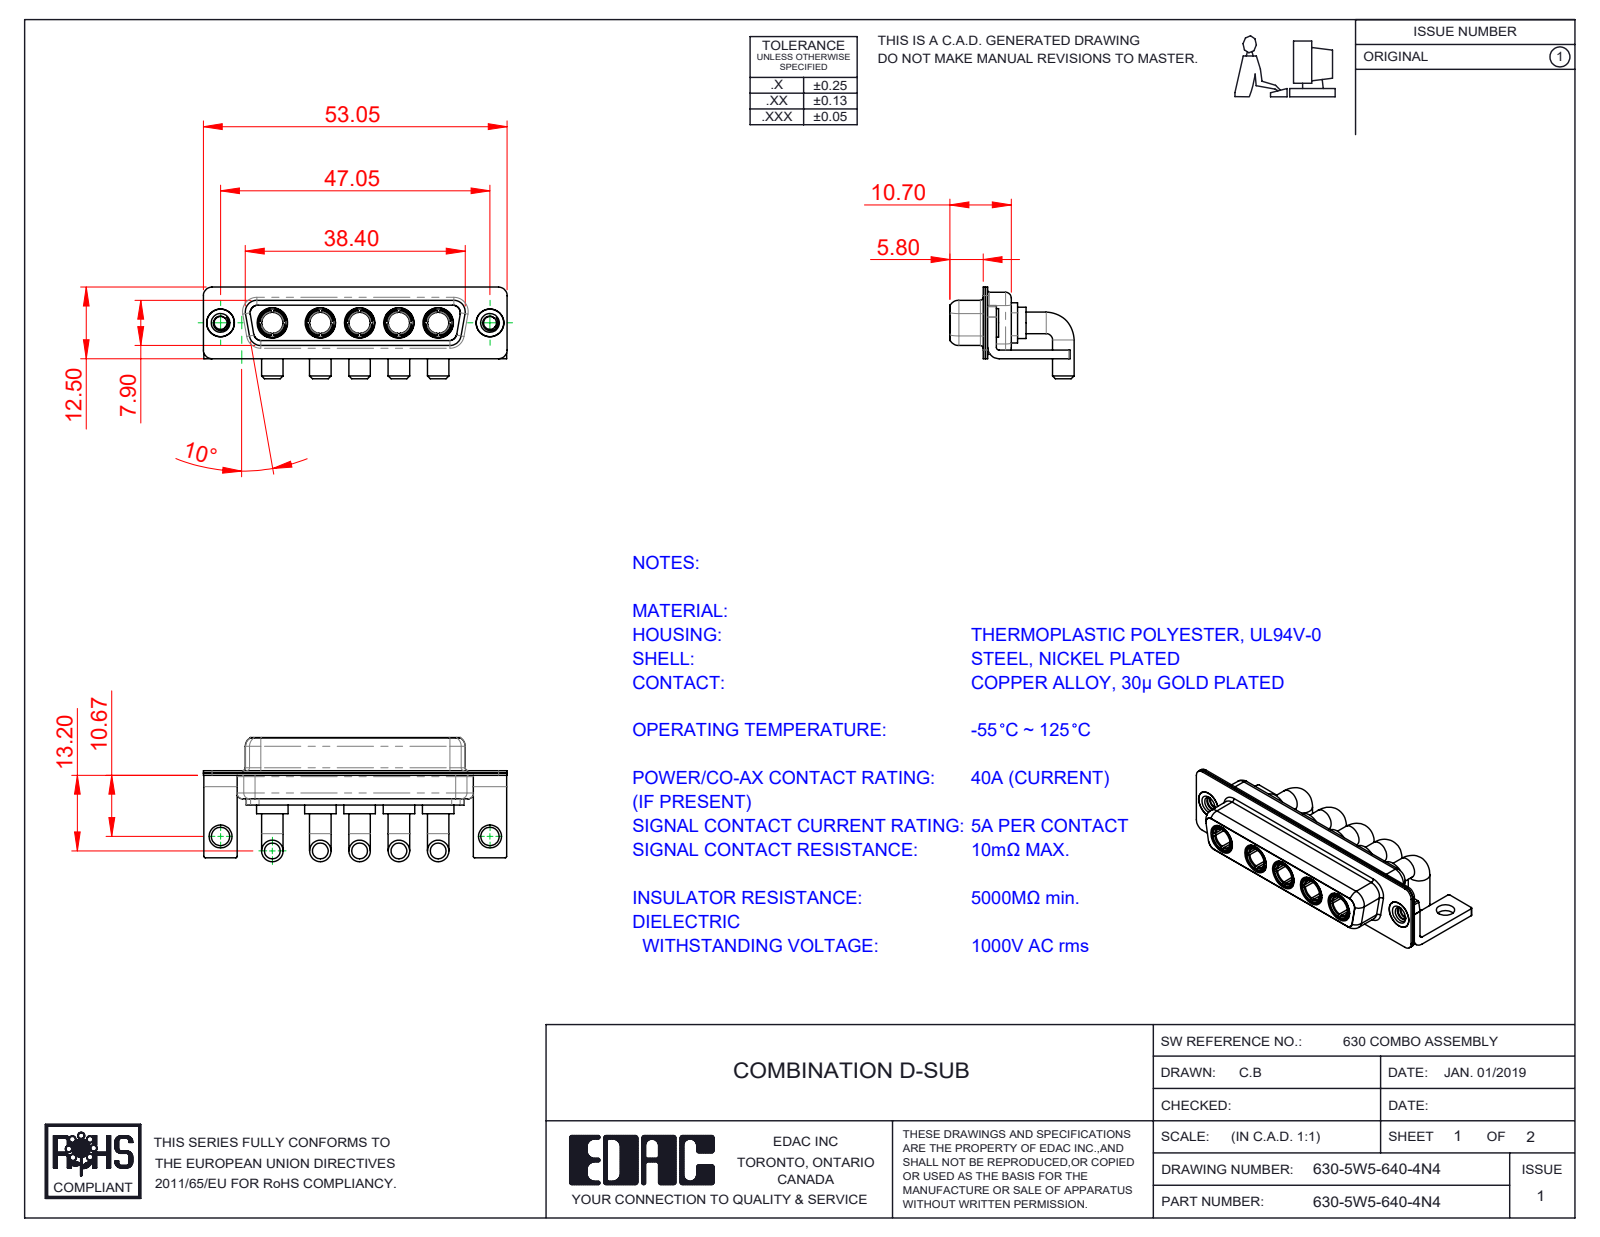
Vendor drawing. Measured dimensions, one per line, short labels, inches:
name: 630Combo Threaded Rivet_3; Power Socket_40A RA; 630Combo Stabilizer Bracket; 630-5W5-640-4N4 (+3 more)
written by: SolidWorks 2020 (CONFIG_CONTROL_DESIGN)
unit: in
bodies: 17 solids, 709 faces (232 planar, 280 cylindrical, 197 other)
size: 2.089 × 0.854 × 0.63
volume: 0.284 in³; area: 14.71 in²
holes: 7× ⌀0.191, 5× ⌀0.146, 5× ⌀0.209, 2× ⌀0.089, 2× ⌀0.126, 2× ⌀0.157, 2× ⌀0.159
bosses: 10× ⌀0.148, 5× ⌀0.217, 5× ⌀0.205, 5× ⌀0.195, 5× ⌀0.187, 2× ⌀0.197, 2× ⌀0.195, 2× ⌀0.189
rounds: 16× R0.01, 16× R0.059, 13× R0.079, 8× R0.053, 8× R0.063, 5× R0.02, 5× R0.083, 4× R0.024
face distances: 0.016, 0.018, 0.055, 0.333, 0.071, 0.031, 0.35, 0.244, 0.059, 0.278
hole spacings: 0.27, 0.356, 1.496, 1.852, 0.27, 0.33, 0.54, 0.541
